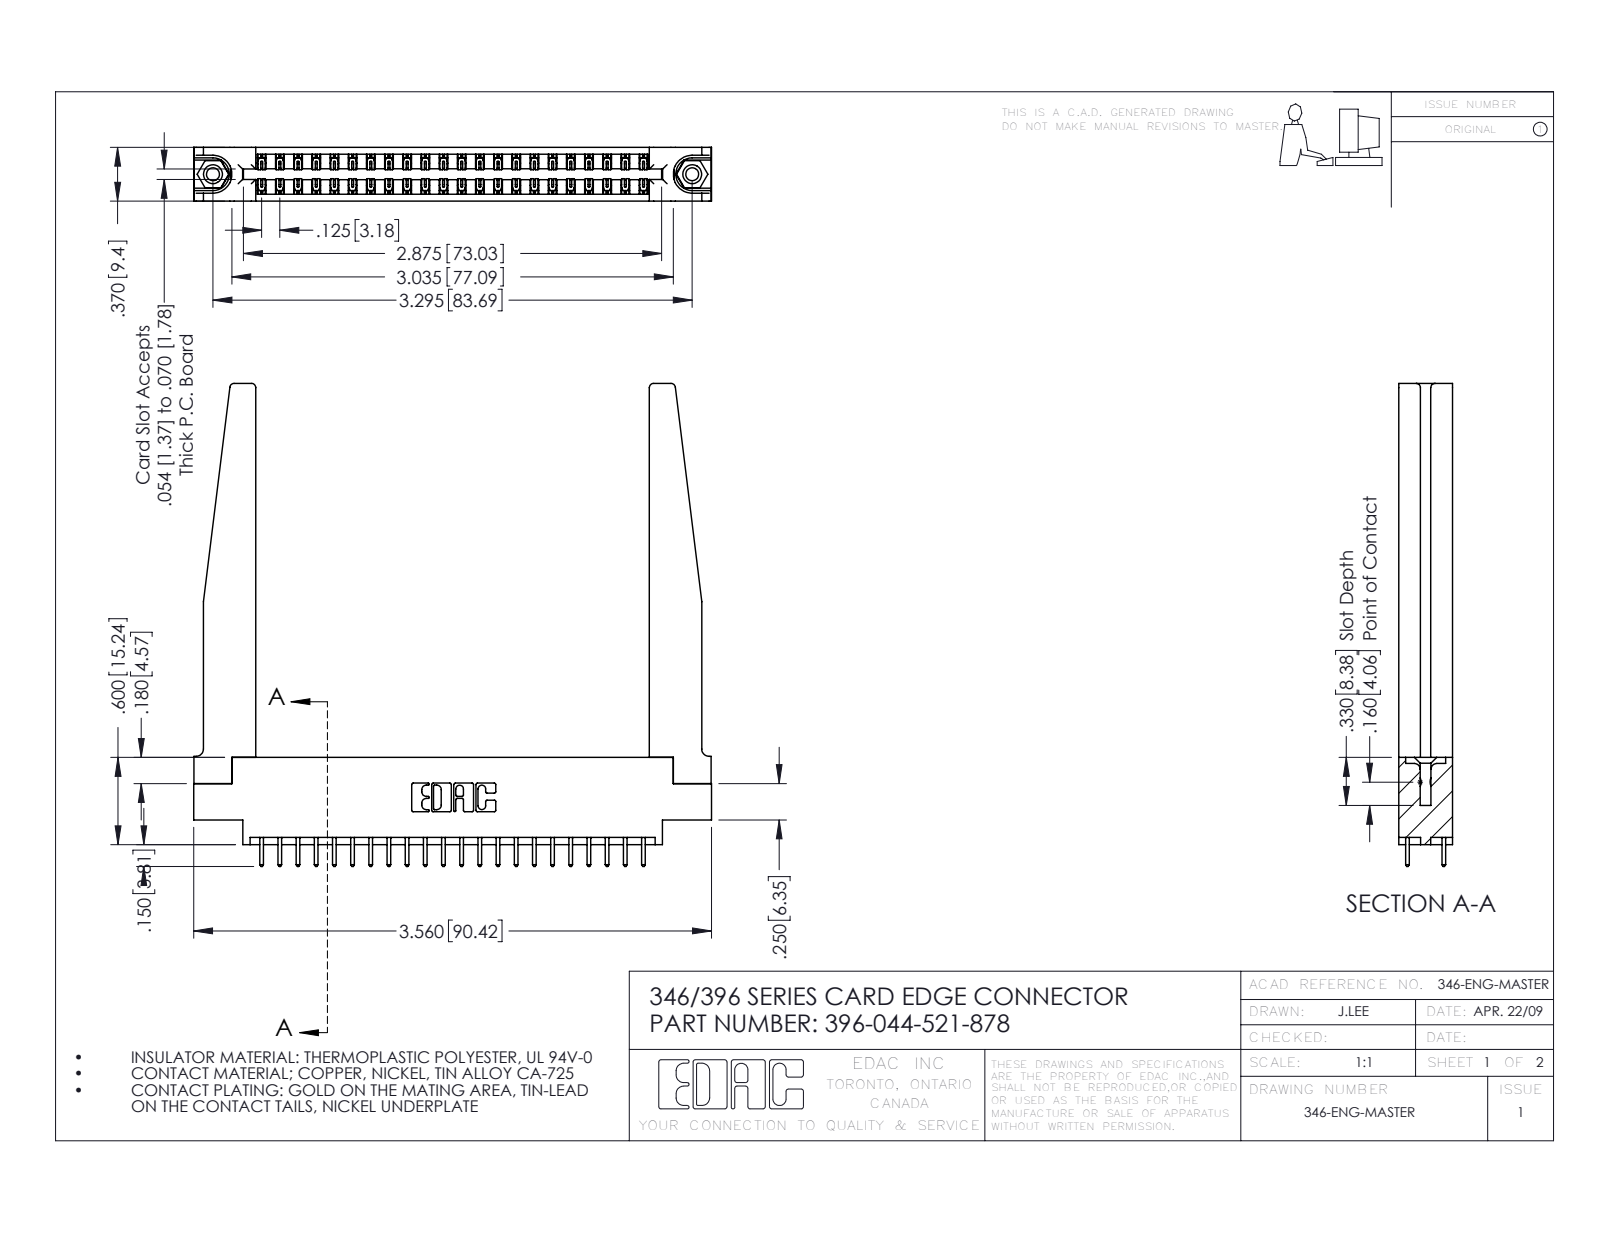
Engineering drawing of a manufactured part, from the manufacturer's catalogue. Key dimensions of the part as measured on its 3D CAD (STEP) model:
Part name (STEP PRODUCT): 345-292-001_345-293-121; 345-250-001_345-250-001-102; 396-044-521-878; 346-220-078_345-220-078 (+1 more)
STEP written by: SolidWorks 2016 (CONFIG_CONTROL_DESIGN)
Units: inches
Bodies: 49 solids, 2648 faces (1762 planar, 834 cylindrical, 52 other)
Overall size (bounding box): 3.56 × 3.32 × 0.37
Volume: 0.94 in³ · Surface area: 27.82 in²
Round holes (diameter × count): ⌀0.089 ×2, ⌀0.125 ×2, ⌀0.156 ×2, ⌀0.064 ×1
Round bosses / shafts (diameter × count): ⌀0.155 ×2
Partial cylindrical surfaces — rounded edges, fillets, slot ends (radius × count): R0.006 ×66, R0.01 ×44, R0.01 ×22, R0.03 ×8, R0.007 ×6, R0.031 ×6, R0.026 ×3, R0.014 ×2
Main face-to-face distances: 0.37, 0.048, 0.322, 0.072, 0.148, 0.15, 0.25, 0.298, 0.025, 0.275
Hole centre spacings: 0.246, 3.087, 3.295
